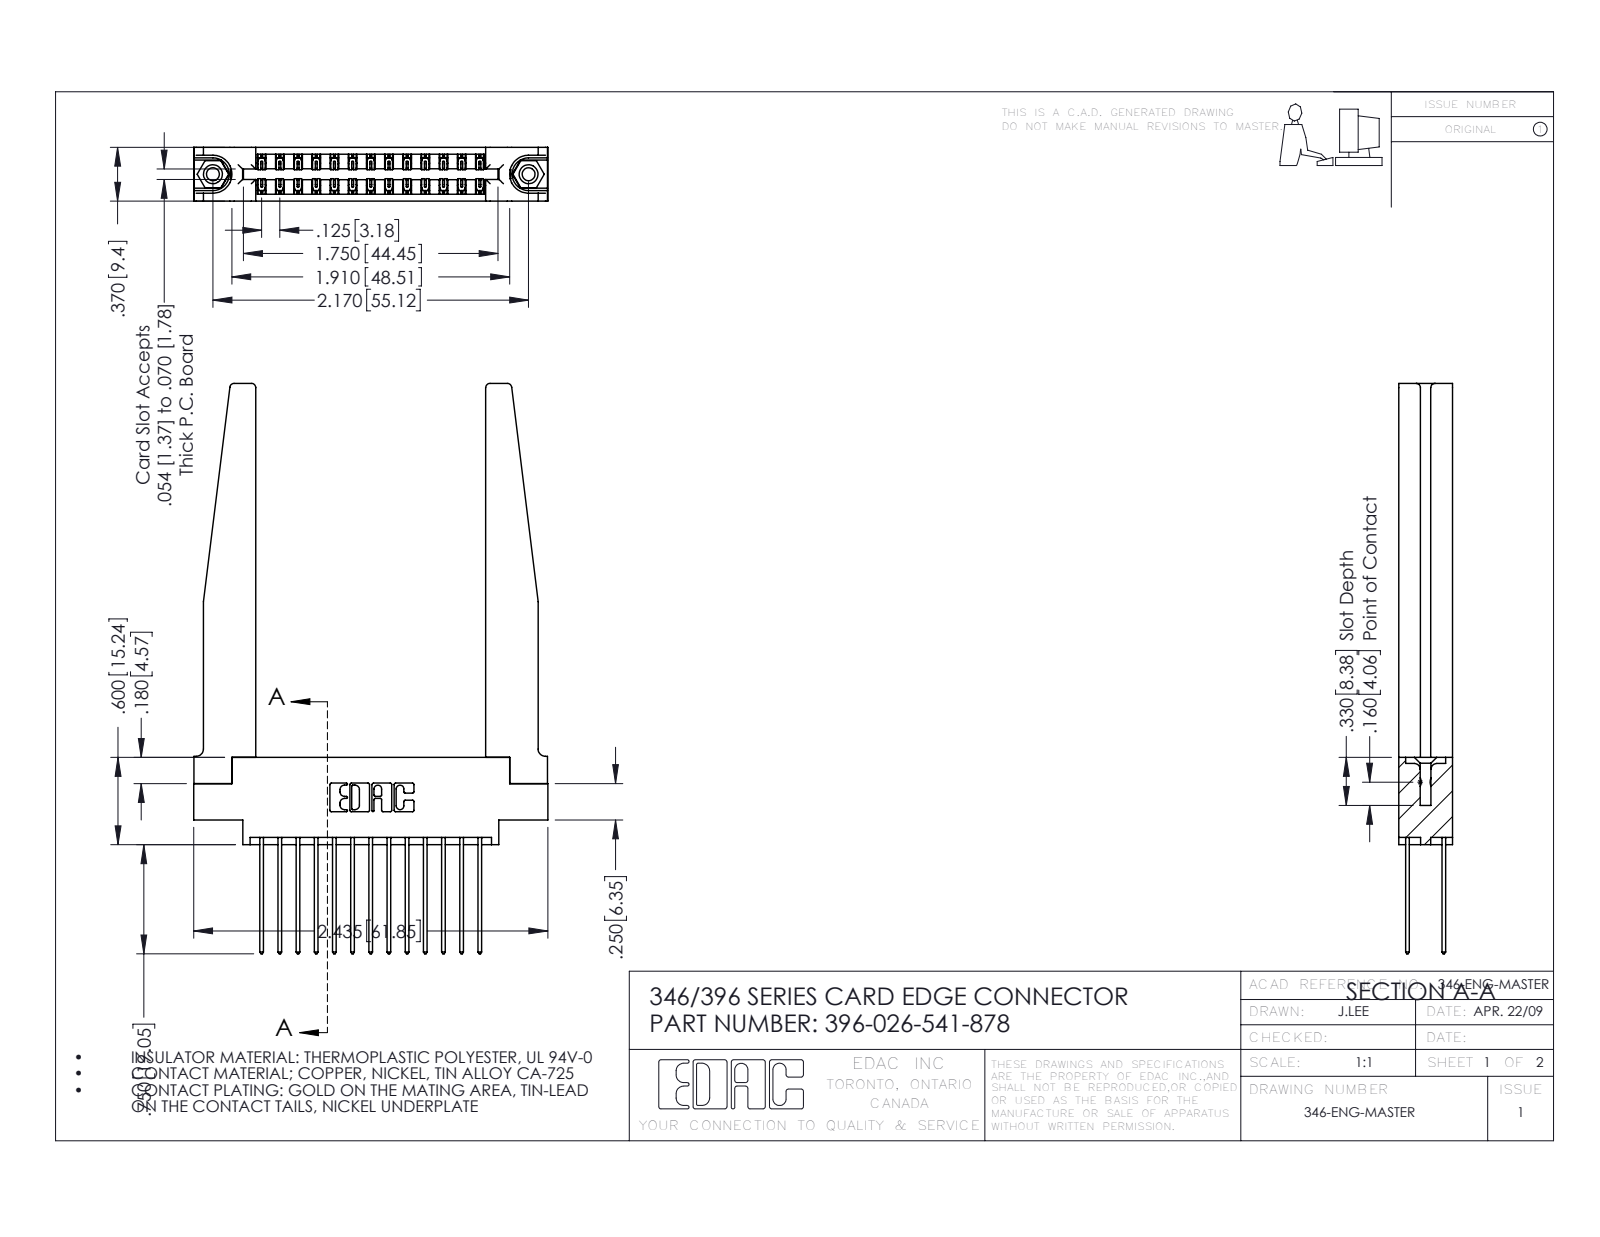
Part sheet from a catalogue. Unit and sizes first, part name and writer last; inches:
Units: inches
Overall size (bounding box): 3.92 × 2.435 × 0.37
Round holes (diameter × count): ⌀0.089 ×2, ⌀0.125 ×2, ⌀0.156 ×2, ⌀0.064 ×1
Round bosses / shafts (diameter × count): ⌀0.155 ×2
Partial cylindrical surfaces — rounded edges, fillets, slot ends (radius × count): R0.006 ×39, R0.01 ×26, R0.01 ×22, R0.03 ×8, R0.007 ×6, R0.031 ×6, R0.026 ×3, R0.014 ×2
Main face-to-face distances: 0.37, 0.072, 0.048, 0.322, 0.148, 0.15, 0.25, 0.298, 0.025, 0.102
Hole centre spacings: 0.246, 1.964, 2.17
Volume: 0.776 in³ · Surface area: 23.17 in²
Bodies: 31 solids, 1712 faces (1132 planar, 528 cylindrical, 52 other)
Part name (STEP PRODUCT): 345-250-001_345-250-001-102; 396-026-541-878; 345-292-001_345-293-141; 346 Part_0.170 Offset - 0.156 Dia-TH (+1 more)
STEP written by: SolidWorks 2016 (CONFIG_CONTROL_DESIGN)
